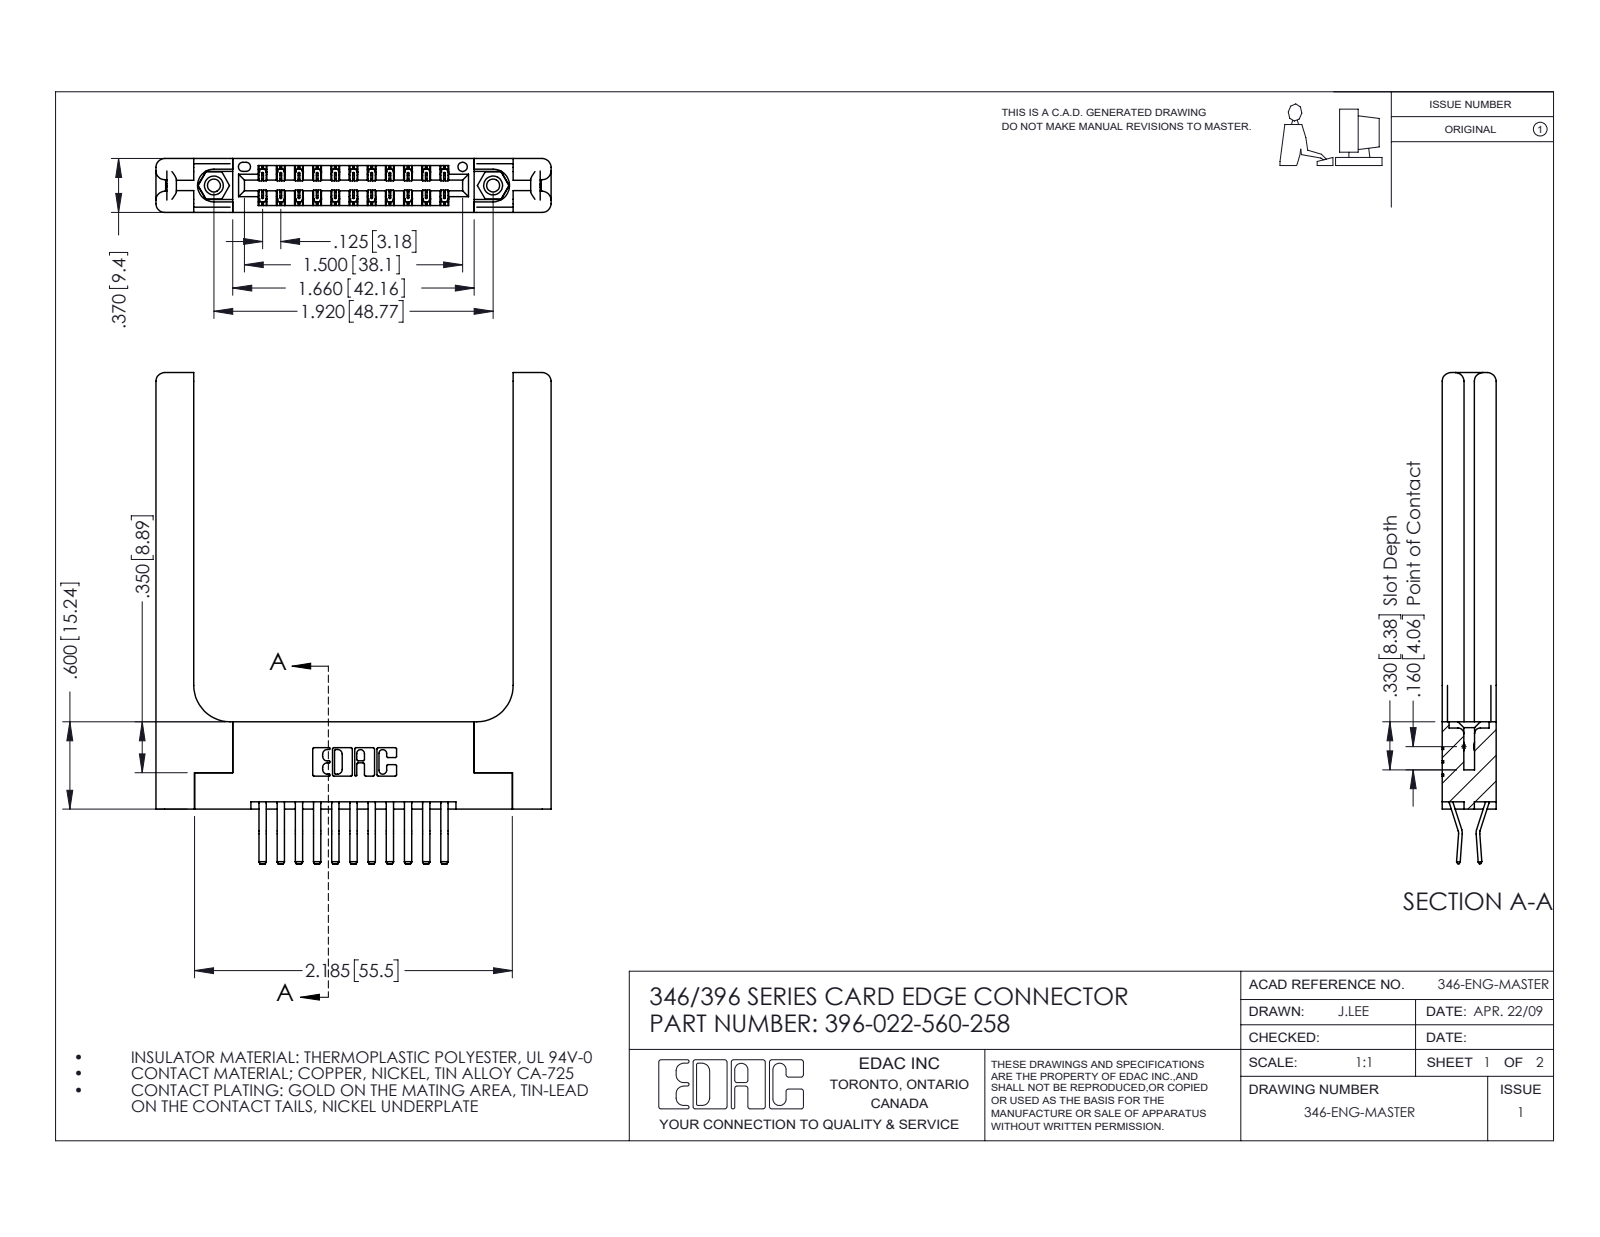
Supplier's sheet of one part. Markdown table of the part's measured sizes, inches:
| quantity | value |
| --- | --- |
| part name | 396-022-560-258; 346-220-058_345-220-058; 346 Part_Flush Mounting Lugs - 0.156 Dia-TH; 345-250-001_345-250-001-102 (+1 more) |
| STEP written by | SolidWorks 2016 (CONFIG_CONTROL_DESIGN) |
| units | inches |
| bodies | 27 solids, 1566 faces (994 planar, 512 cylindrical, 60 other) |
| overall size | 3.375 × 2.716 × 0.37 |
| volume | 0.862 in³ |
| surface area | 21.68 in² |
| round holes (diameter × count) | 0.089 × 2, 0.125 × 2, 0.156 × 2, 0.064 × 1 |
| round bosses / shafts (diameter × count) | 0.155 × 2 |
| partial cylindrical surfaces (radius × count) | 0.006 × 33, 0.01 × 22, 0.06 × 16, 0.007 × 6, 0.031 × 6, 0.026 × 3, 0.01 × 2, 0.014 × 2 |
| main face-to-face distances | 0.37, 0.15, 0.072, 0.148, 0.22, 0.102, 0.048, 0.322, 0.173, 0.25 |
| hole center spacings | 0.246, 1.715, 1.92 |
